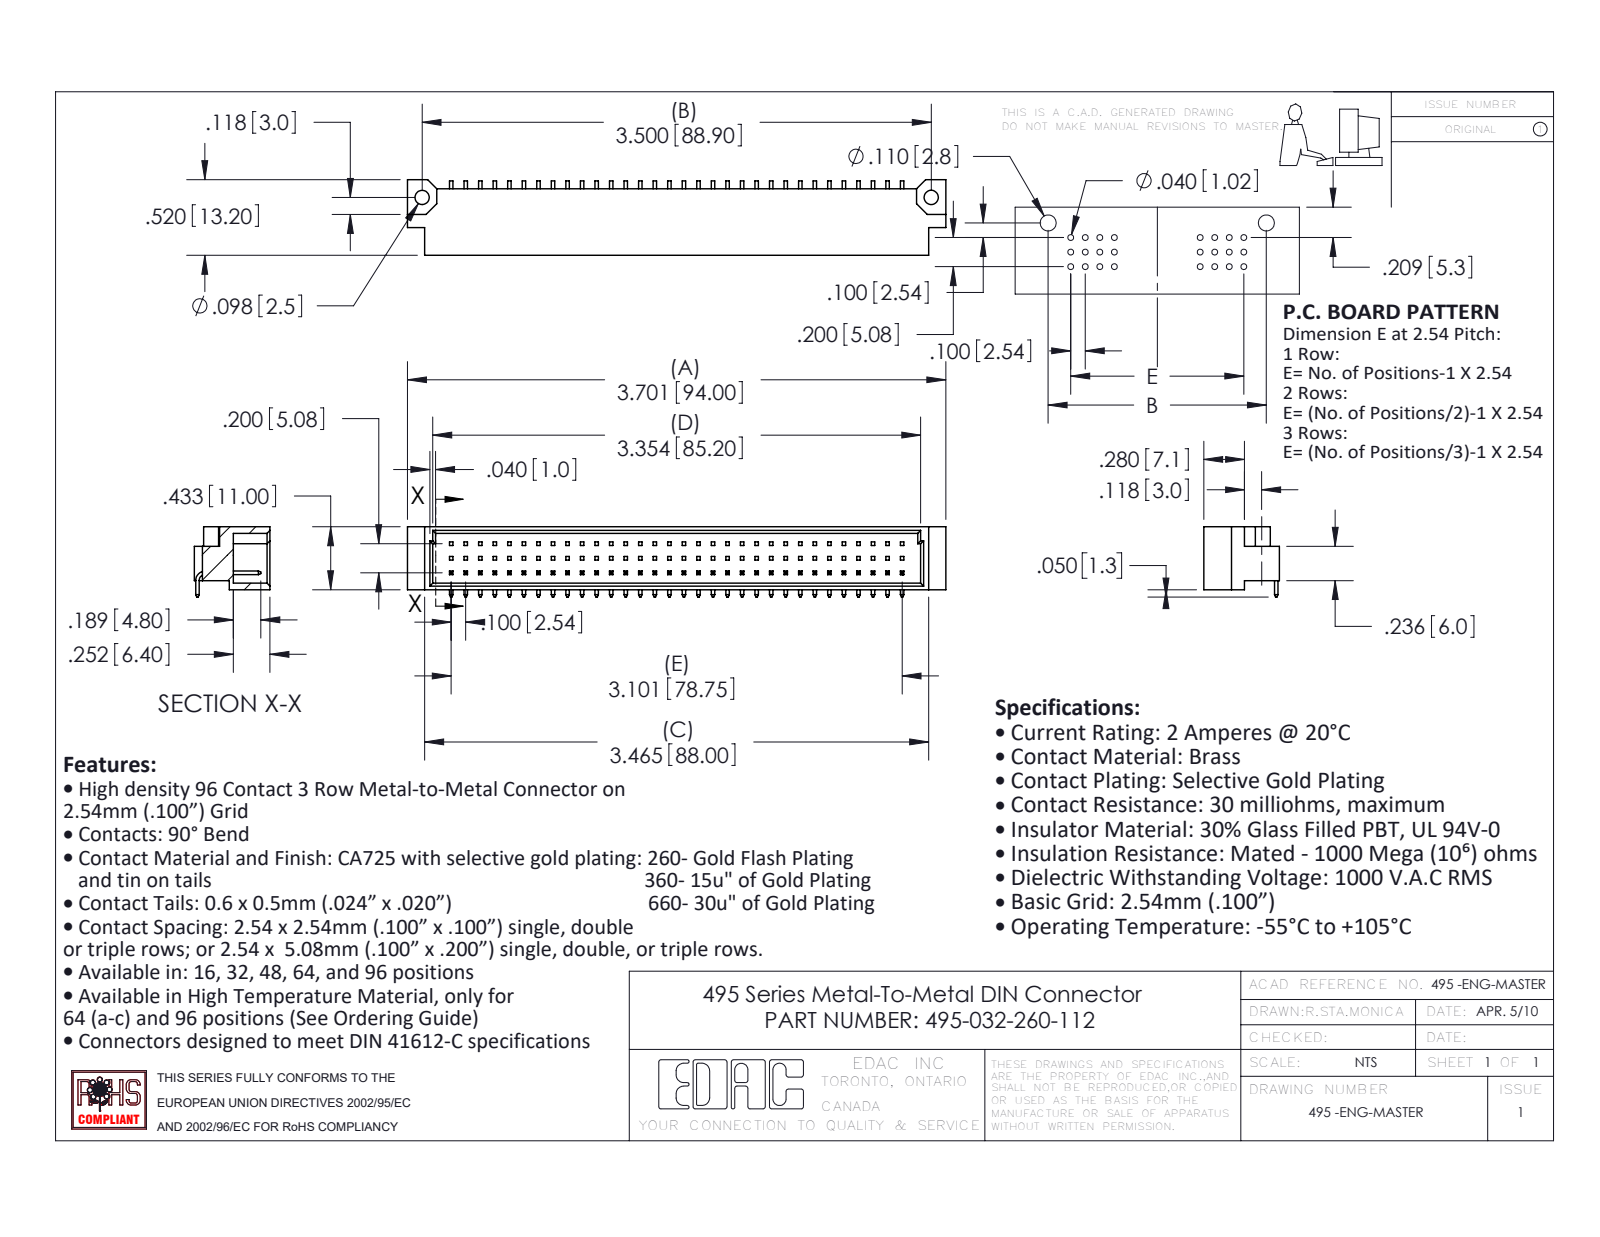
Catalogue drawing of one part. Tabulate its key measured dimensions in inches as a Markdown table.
| quantity | value |
| --- | --- |
| part name | 495 Part_96; 495-290-3; 495-032-260-112 |
| STEP written by | SolidWorks 2020 (AUTOMOTIVE_DESIGN) |
| units | inches |
| bodies | 33 solids, 1009 faces (941 planar, 68 cylindrical, 0 other) |
| overall size | 3.701 × 0.52 × 0.483 |
| volume | 0.372 in³ |
| surface area | 12.37 in² |
| round holes (diameter × count) | 0.098 × 2 |
| partial cylindrical surfaces (radius × count) | 0.04 × 1, 0.065 × 1 |
| main face-to-face distances | 0.045, 0.388, 0.205, 0.433, 0.1, 0.024, 0.343, 0.063, 0.37, 0.018 |
| hole center spacings | 3.5 |
